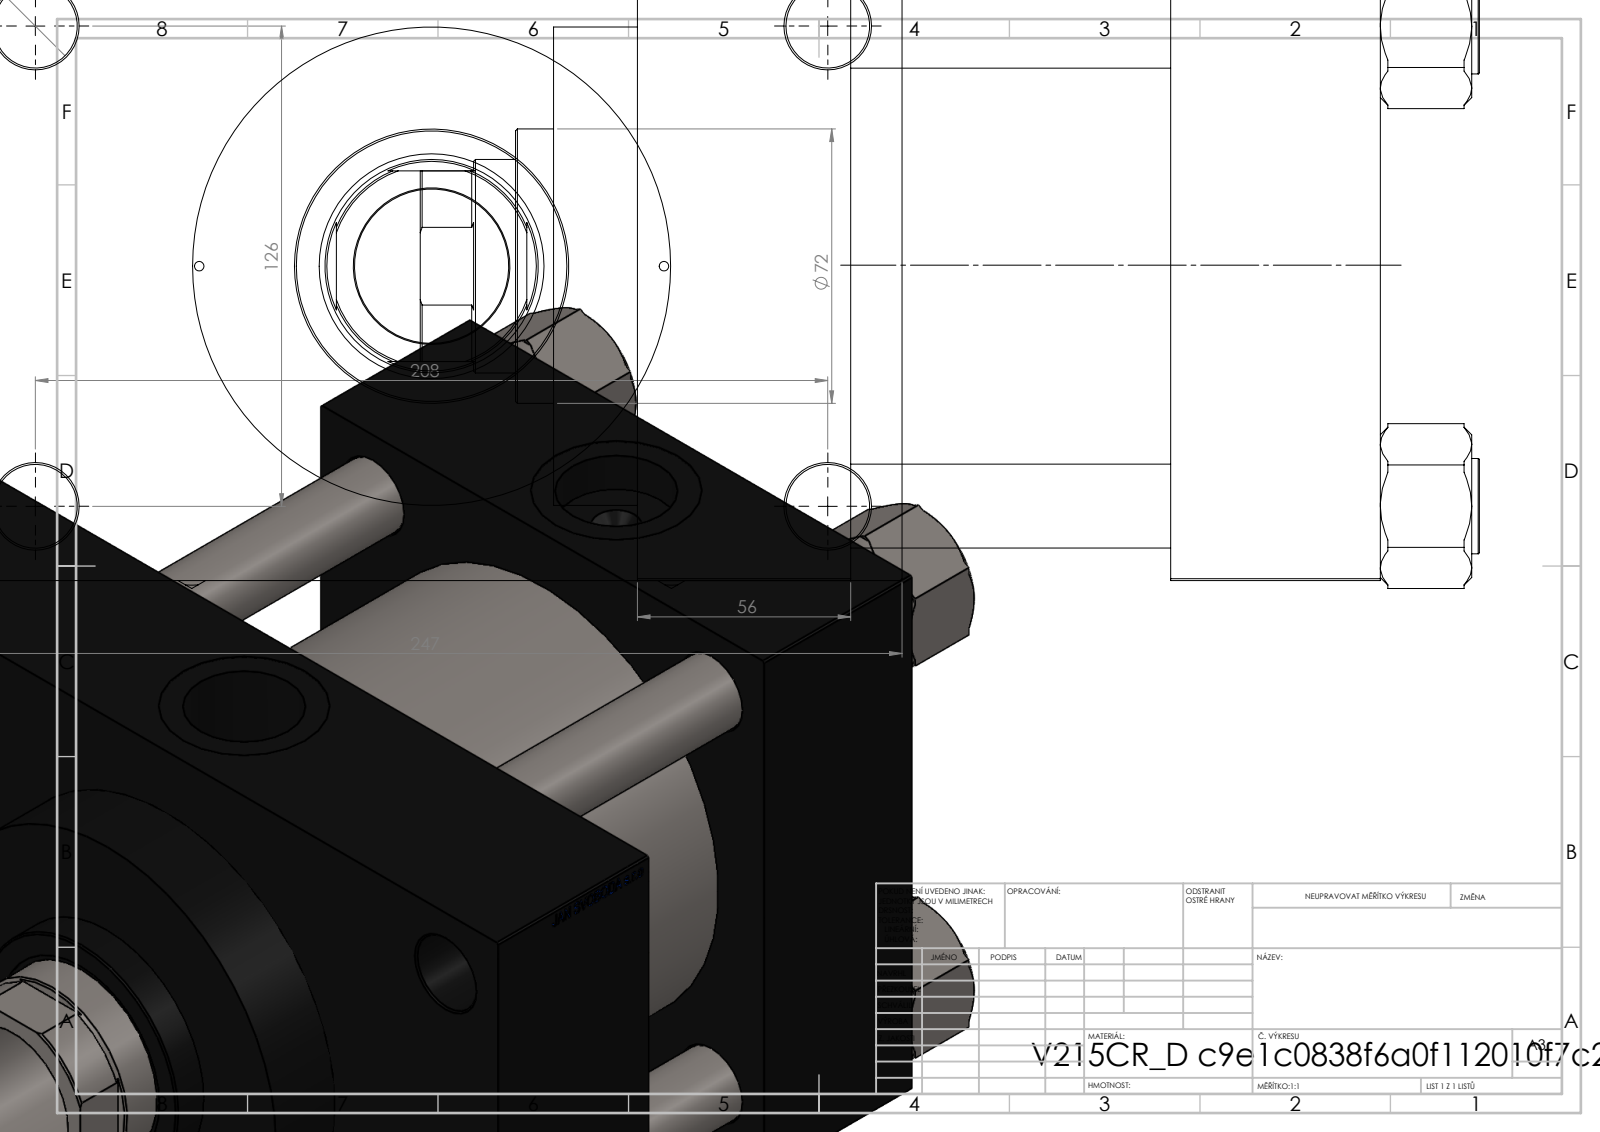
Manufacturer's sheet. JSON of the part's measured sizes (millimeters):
{"part_name": "V215CR_D_Body; V215CR_VCP_D; V215CR_D_TYCINKA; NUT_M5_D (+1 more)", "step_written_by": "SolidWorks 2019 (CONFIG_CONTROL_DESIGN)", "units": "millimeters", "bodies": {"solids": 11, "faces": 1155, "planar": 546, "cylindrical": 91, "other": 518}, "overall_size": [278, 247, 169.14], "volume_mm3": 4958000, "surface_area_mm2": 529995, "round_holes": [[22, 8], [2.5, 2], [7, 2], [32.24, 2], [45, 2], [40.5, 1], [56, 1], [59, 1], [96, 1], [125, 1], [125.5, 1]], "round_bosses_or_shafts": [[25, 4], [131, 1], [72, 1]], "partial_cylinders_radius": [[27, 1]], "face_to_face_distances": [165, 84, 55, 139, 56, 195, 140, 41, 206, 173.74], "hole_center_spacings": [41.05, 62.98, 76.28, 89.02, 121.59, 125.9, 132.47, 139.02]}
